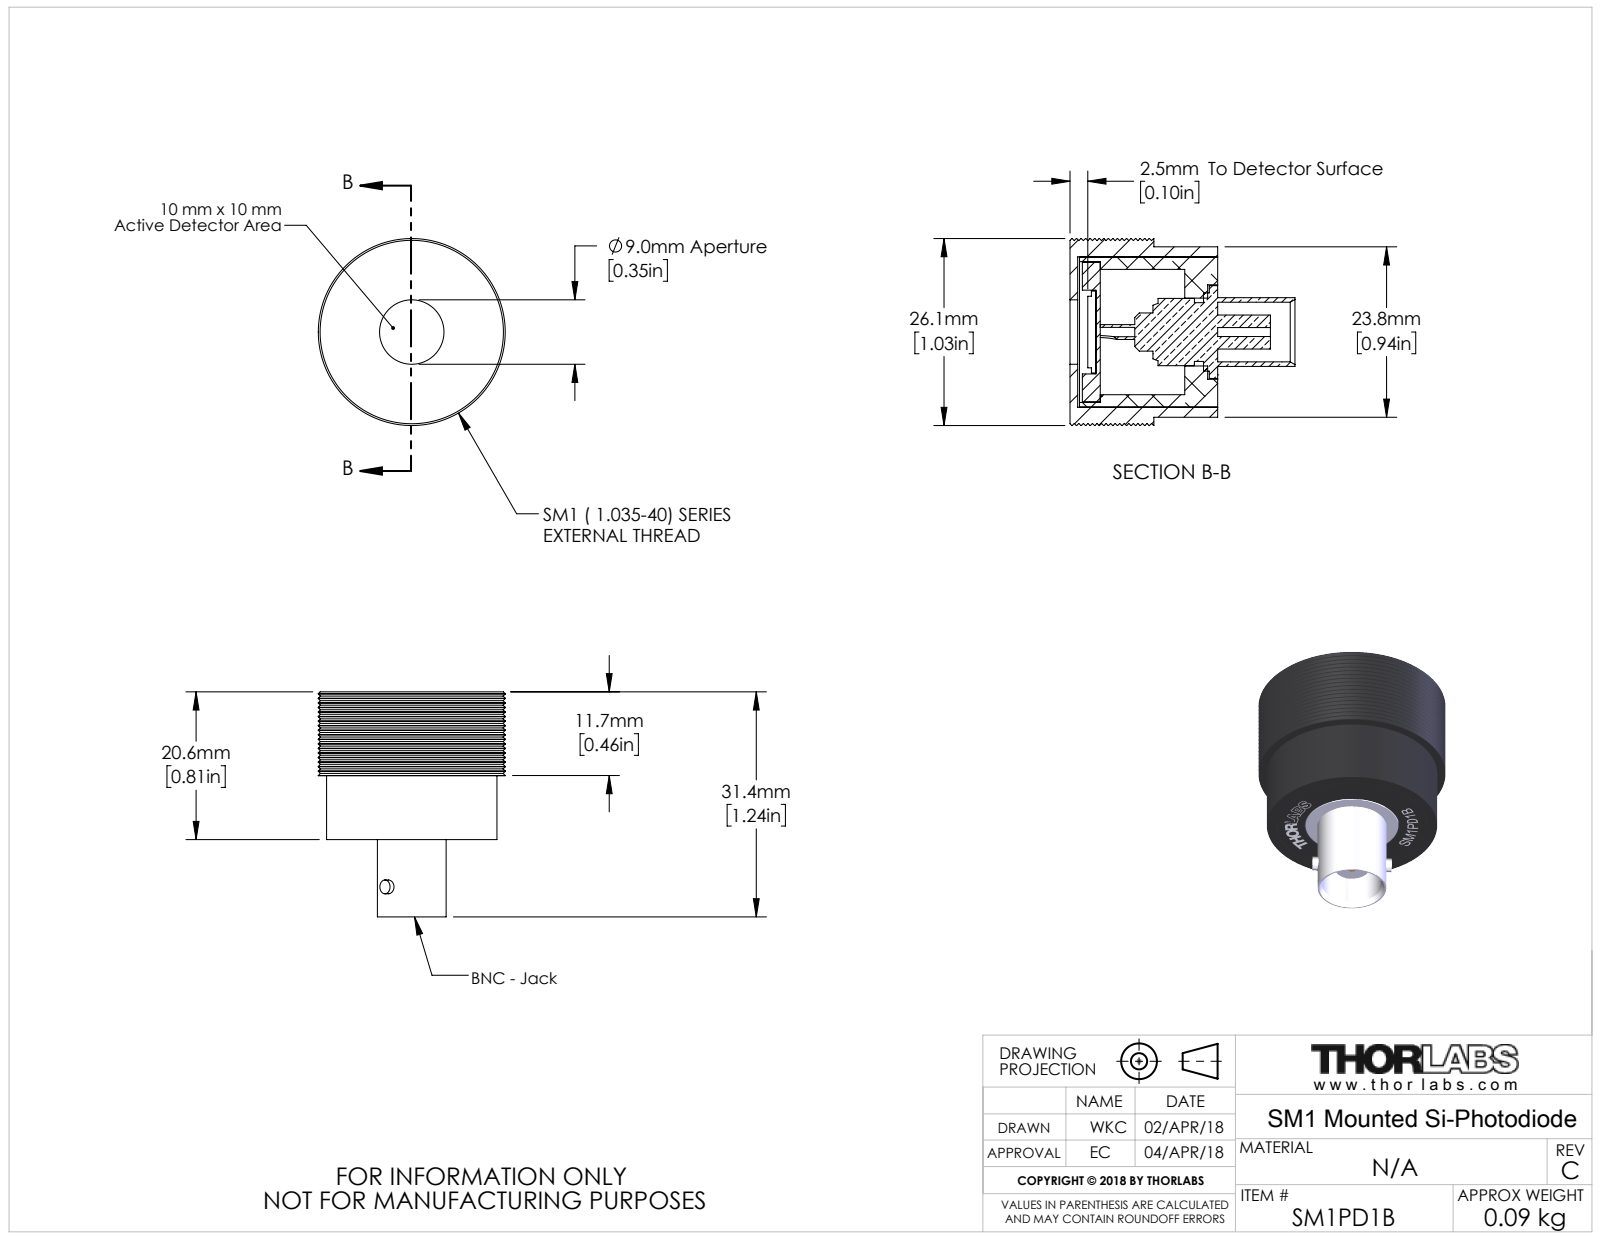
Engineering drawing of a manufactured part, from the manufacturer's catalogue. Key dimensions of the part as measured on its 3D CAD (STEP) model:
Part name (STEP PRODUCT): TTN008837-E0W
STEP written by: SolidWorks 2016 (AUTOMOTIVE_DESIGN)
Units: inches
Bodies: 5 solids, 413 faces (217 planar, 43 cylindrical, 153 other)
Overall size (bounding box): 1.237 × 1.028 × 1.028
Volume: 0.45 in³ · Surface area: 14.78 in²
Round holes (diameter × count): ⌀0.05 ×1, ⌀0.052 ×1, ⌀0.328 ×1, ⌀0.354 ×1, ⌀0.373 ×1, ⌀0.52 ×1, ⌀0.689 ×1, ⌀0.774 ×1, ⌀0.827 ×1
Round bosses / shafts (diameter × count): ⌀1.028 ×1, ⌀0.937 ×1, ⌀0.824 ×1, ⌀0.766 ×1, ⌀0.51 ×1, ⌀0.43 ×1, ⌀0.378 ×1, ⌀0.37 ×1
Partial cylindrical surfaces — rounded edges, fillets, slot ends (radius × count): R0.039 ×2
Main face-to-face distances: 0.812, 0.646, 0.167, 0.669, 0.024, 0.143, 0.77, 0.124, 0.101, 0.042
